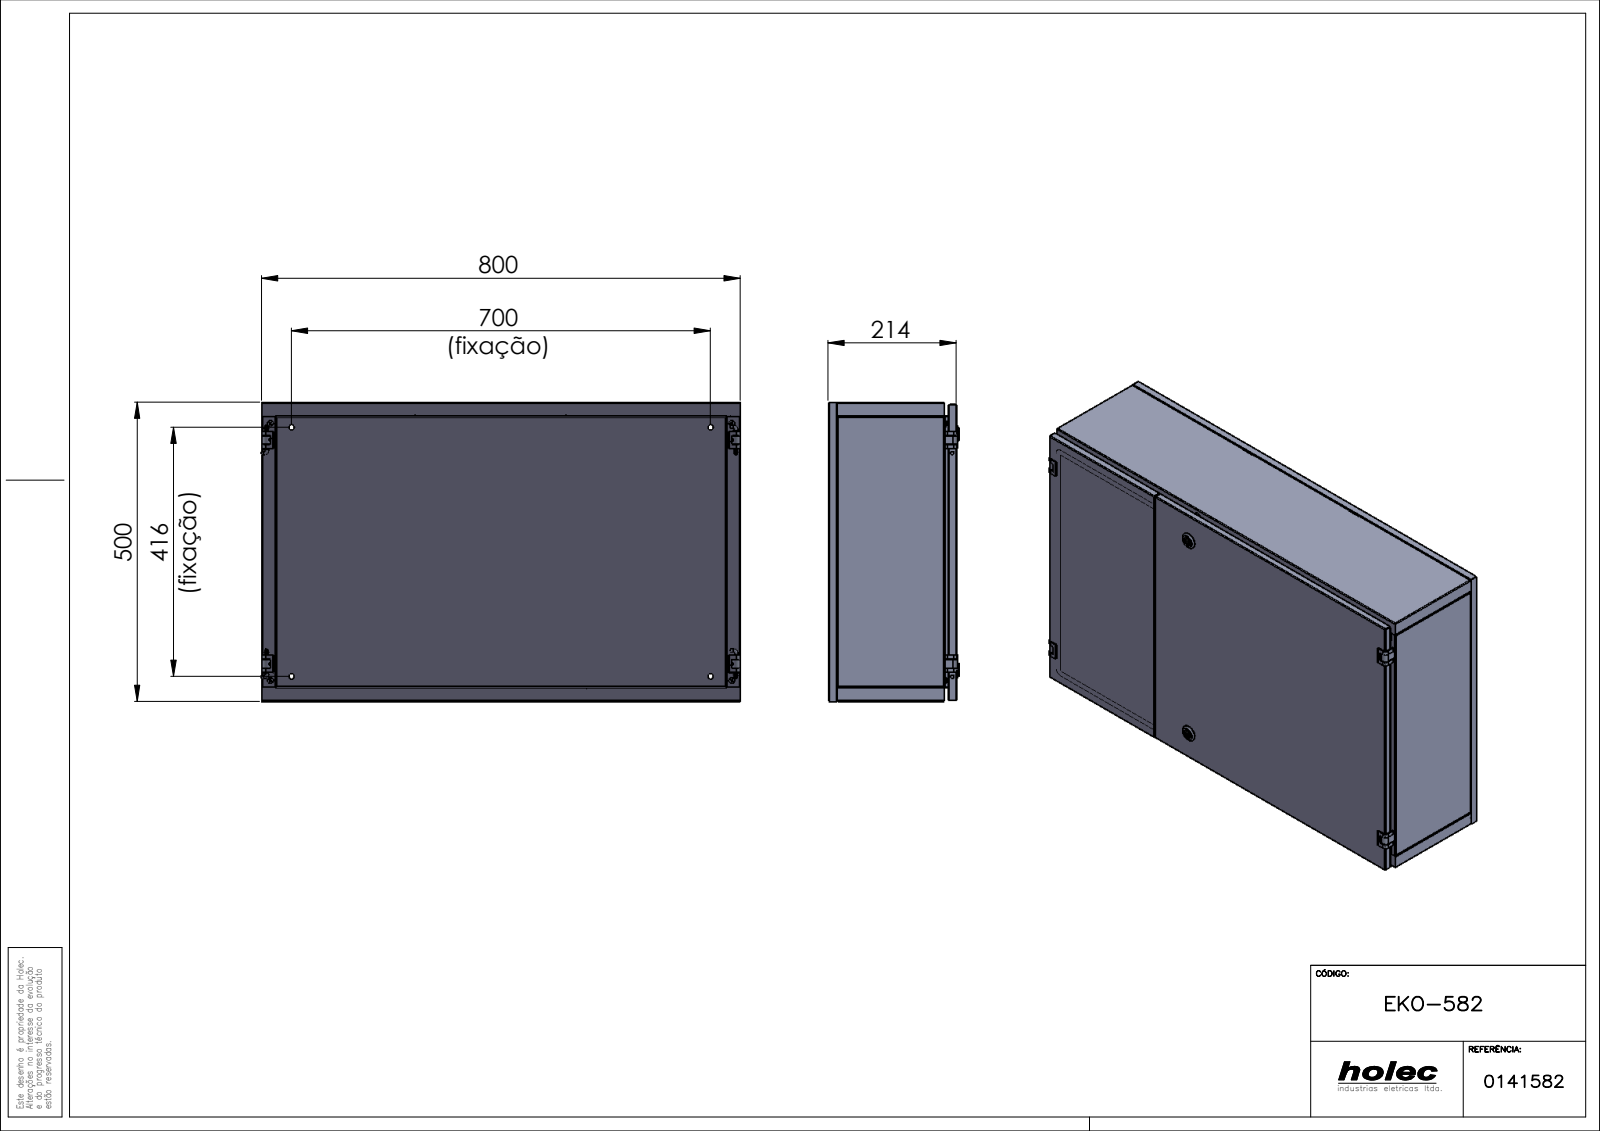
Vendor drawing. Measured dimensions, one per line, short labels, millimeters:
name: EKO-582
written by: SolidWorks 2017 (AUTOMOTIVE_DESIGN)
unit: mm
bodies: 60 solids, 3795 faces (1883 planar, 1178 cylindrical, 734 other)
size: 801 × 500 × 218.1
volume: 1 823 000 mm³; area: 3 507 000 mm²
holes: 36× ⌀4.3, 14× ⌀6, 12× ⌀4.2, 8× ⌀5.5, 8× ⌀11, 6× ⌀5, 4× ⌀3.3, 4× ⌀4, 4× ⌀9, 2× ⌀4.1, 2× ⌀10, 2× ⌀10.1
bosses: 8× ⌀10, 8× ⌀5, 4× ⌀4, 2× ⌀28, 2× ⌀19, 2× ⌀15.7, 2× ⌀15, 2× ⌀12.7
rounds: 152× R0.2, 59× R1.5, 57× R0.5, 40× R0.3, 22× R1, 14× R2.5, 8× R2, 7× R5
face distances: 1, 213.1, 212.1, 214.1, 499, 799, 500, 498, 24, 22.9
hole spacings: 25, 31.4, 253.24, 252, 50, 53.49, 256.91, 19
